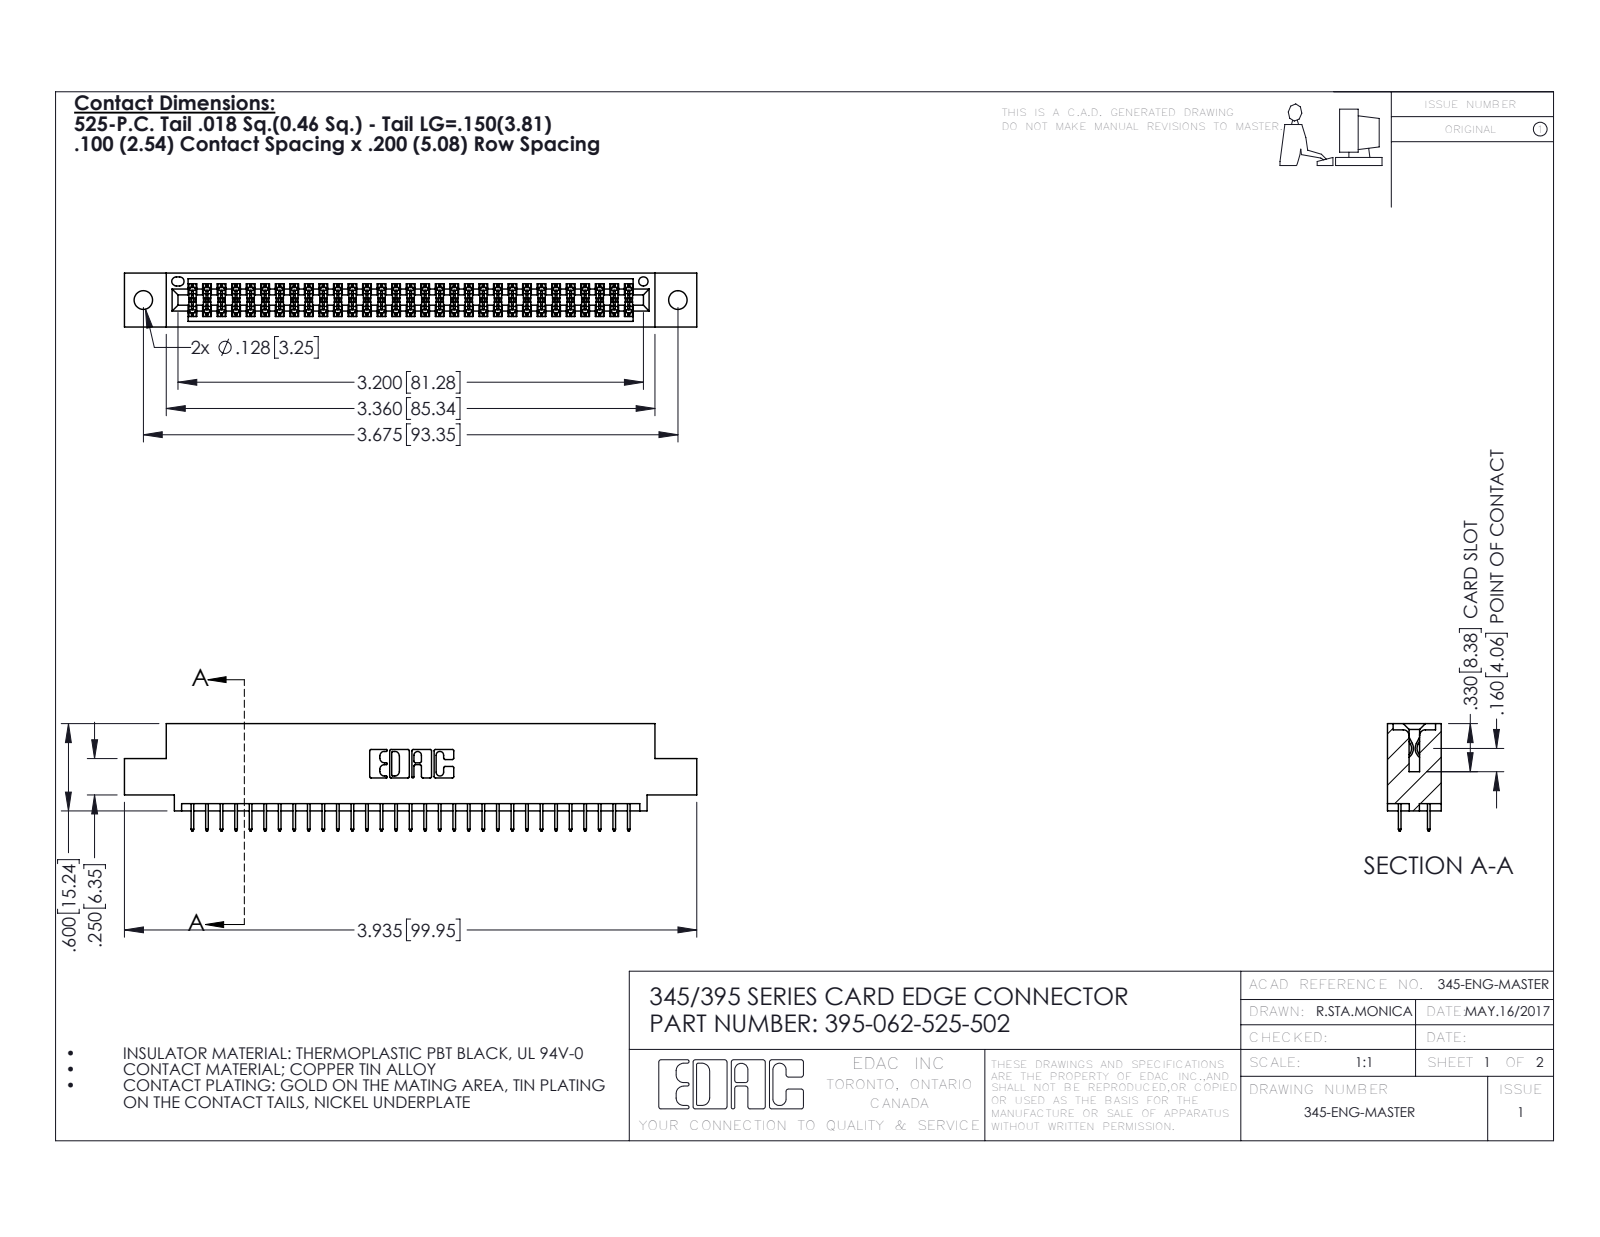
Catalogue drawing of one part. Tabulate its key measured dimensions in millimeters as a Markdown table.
| quantity | value |
| --- | --- |
| part name | 345 Part_0.110 Offset - 0.128 Dia; 395-062-525-502; 345-292-001_345-293-125 |
| STEP written by | SolidWorks 2020 (CONFIG_CONTROL_DESIGN) |
| units | millimeters |
| bodies | 63 solids, 3478 faces (2502 planar, 976 cylindrical, 0 other) |
| overall size | 99.9 × 18.7 × 9.4 |
| volume | 9 390 mm³ |
| surface area | 13 190 mm² |
| round holes (diameter × count) | 3.3 × 2, 1.6 × 1 |
| partial cylindrical surfaces (radius × count) | 0.2 × 93, 0.3 × 22, 0.2 × 6, 0.8 × 6, 0.7 × 3, 0.4 × 2, 0.5 × 2, 0.6 × 2 |
| main face-to-face distances | 1.8, 7.6, 5.1, 9.4, 2.5, 6.9, 0.6, 5.7, 1.8, 4.4 |
| hole center spacings | 6.9, 87.4, 93.3 |
